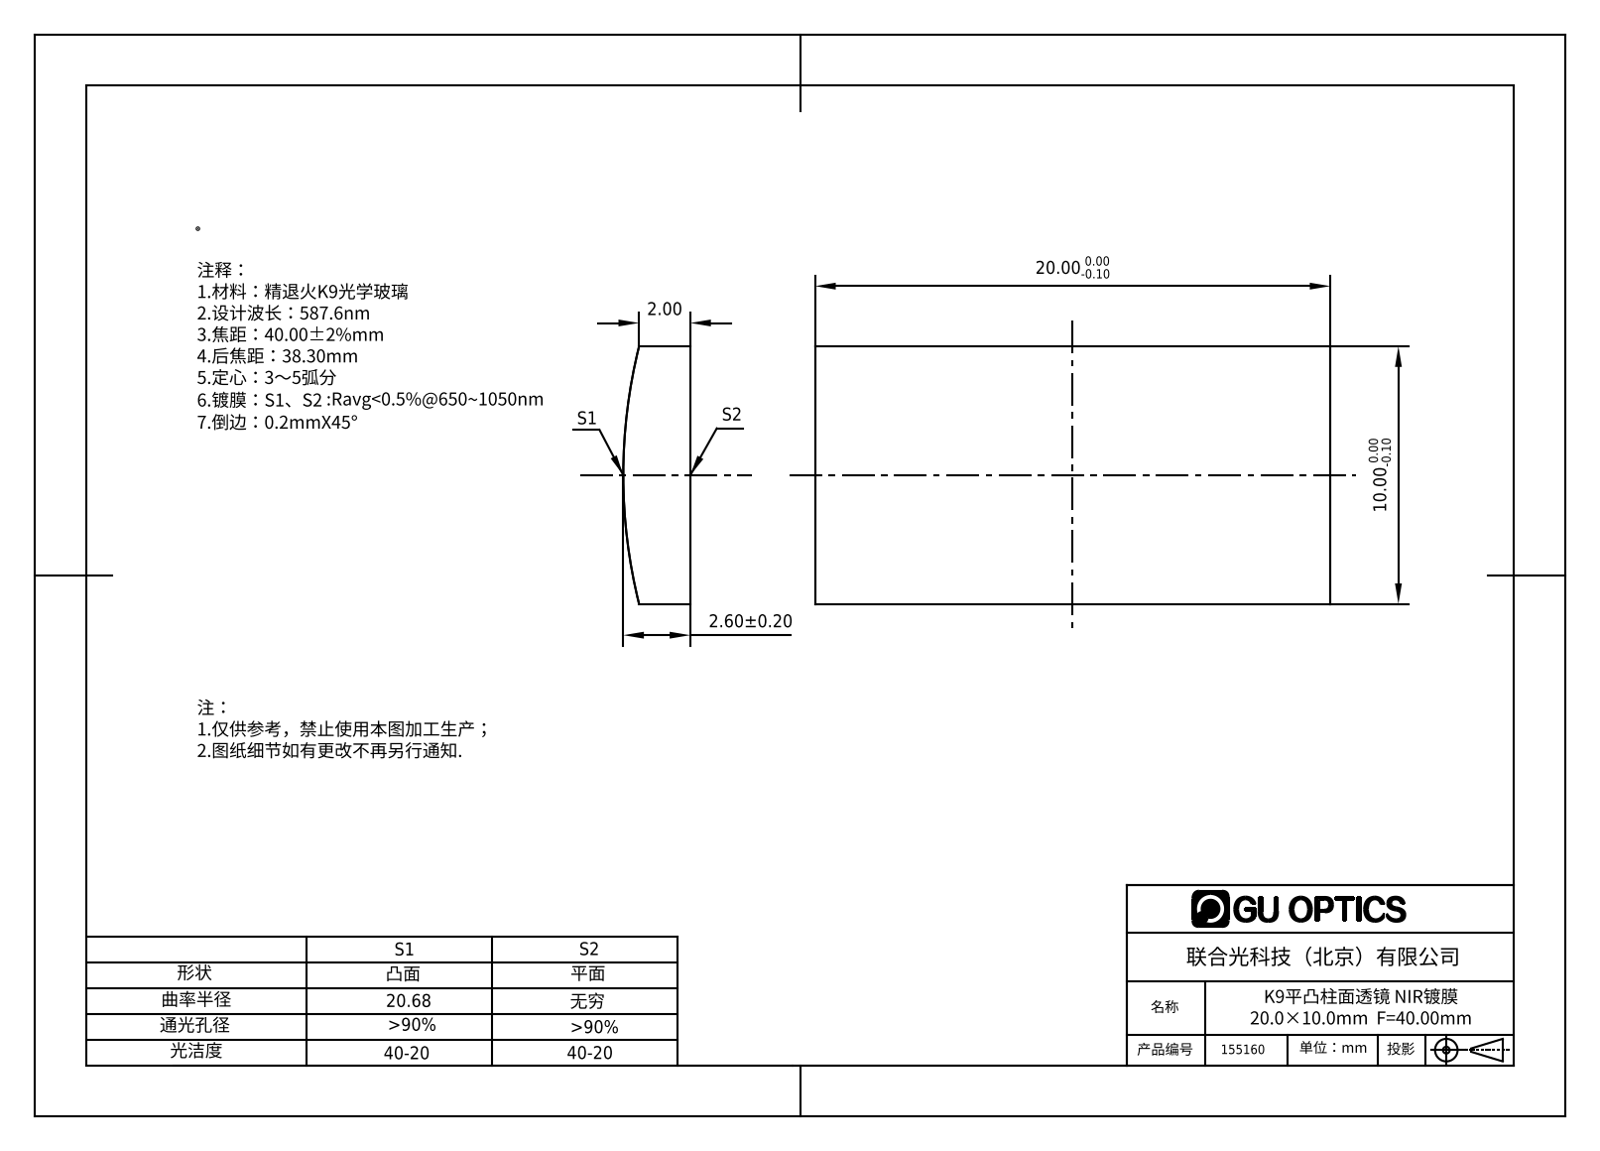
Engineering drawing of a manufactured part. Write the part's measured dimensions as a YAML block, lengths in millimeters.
part_name: "155028"
step_written_by: "SolidWorks 2016 (AUTOMOTIVE_DESIGN)"
units: millimeters
bodies: {solids: 1, faces: 6, planar: 5, cylindrical: 1, other: 0}
overall_size: [20, 10, 2.6]
volume: 479
surface_area: 529
partial_cylinders:
  - {radius: 20.68, count: 1}
face_to_face_distances: [10, 20]
